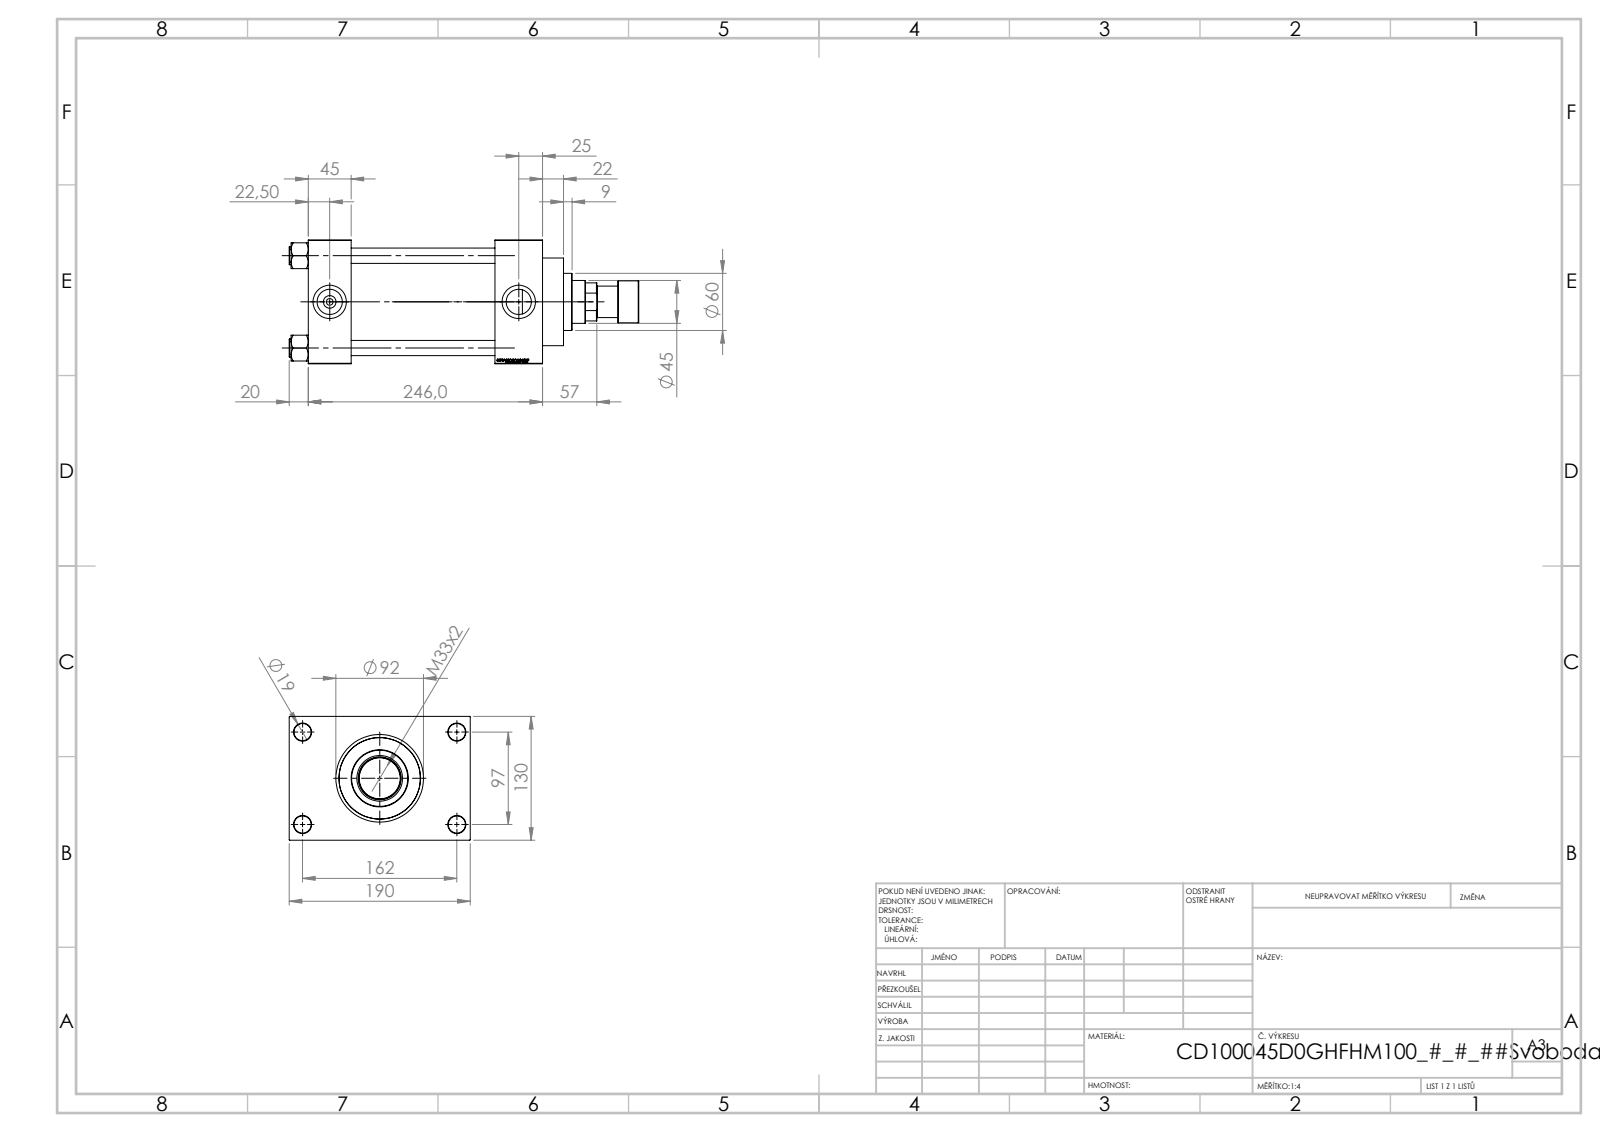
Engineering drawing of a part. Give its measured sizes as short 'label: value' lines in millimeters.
name: V215CD_D_TYCINKA; V215CD_VC_A; V215CR_ROD_END_F; V215CD_D_Body (+2 more)
written by: SolidWorks 2019 (CONFIG_CONTROL_DESIGN)
unit: mm
bodies: 12 solids, 1164 faces (548 planar, 92 cylindrical, 524 other)
size: 367 × 190 × 130
volume: 2 912 000 mm³; area: 442 424 mm²
holes: 4× ⌀16, 4× ⌀18, 2× ⌀7, 2× ⌀26.44, 2× ⌀35, 1× ⌀31.5, 1× ⌀45, 1× ⌀48, 1× ⌀76, 1× ⌀85.5, 1× ⌀100
bosses: 4× ⌀19, 1× ⌀106, 1× ⌀92, 1× ⌀60, 1× ⌀44, 1× ⌀33
face distances: 130, 151, 45, 196, 246, 201, 50, 30, 160, 96
hole spacings: 32.55, 68.52, 94.41, 96.9, 102.27, 129.45, 161.73, 97
